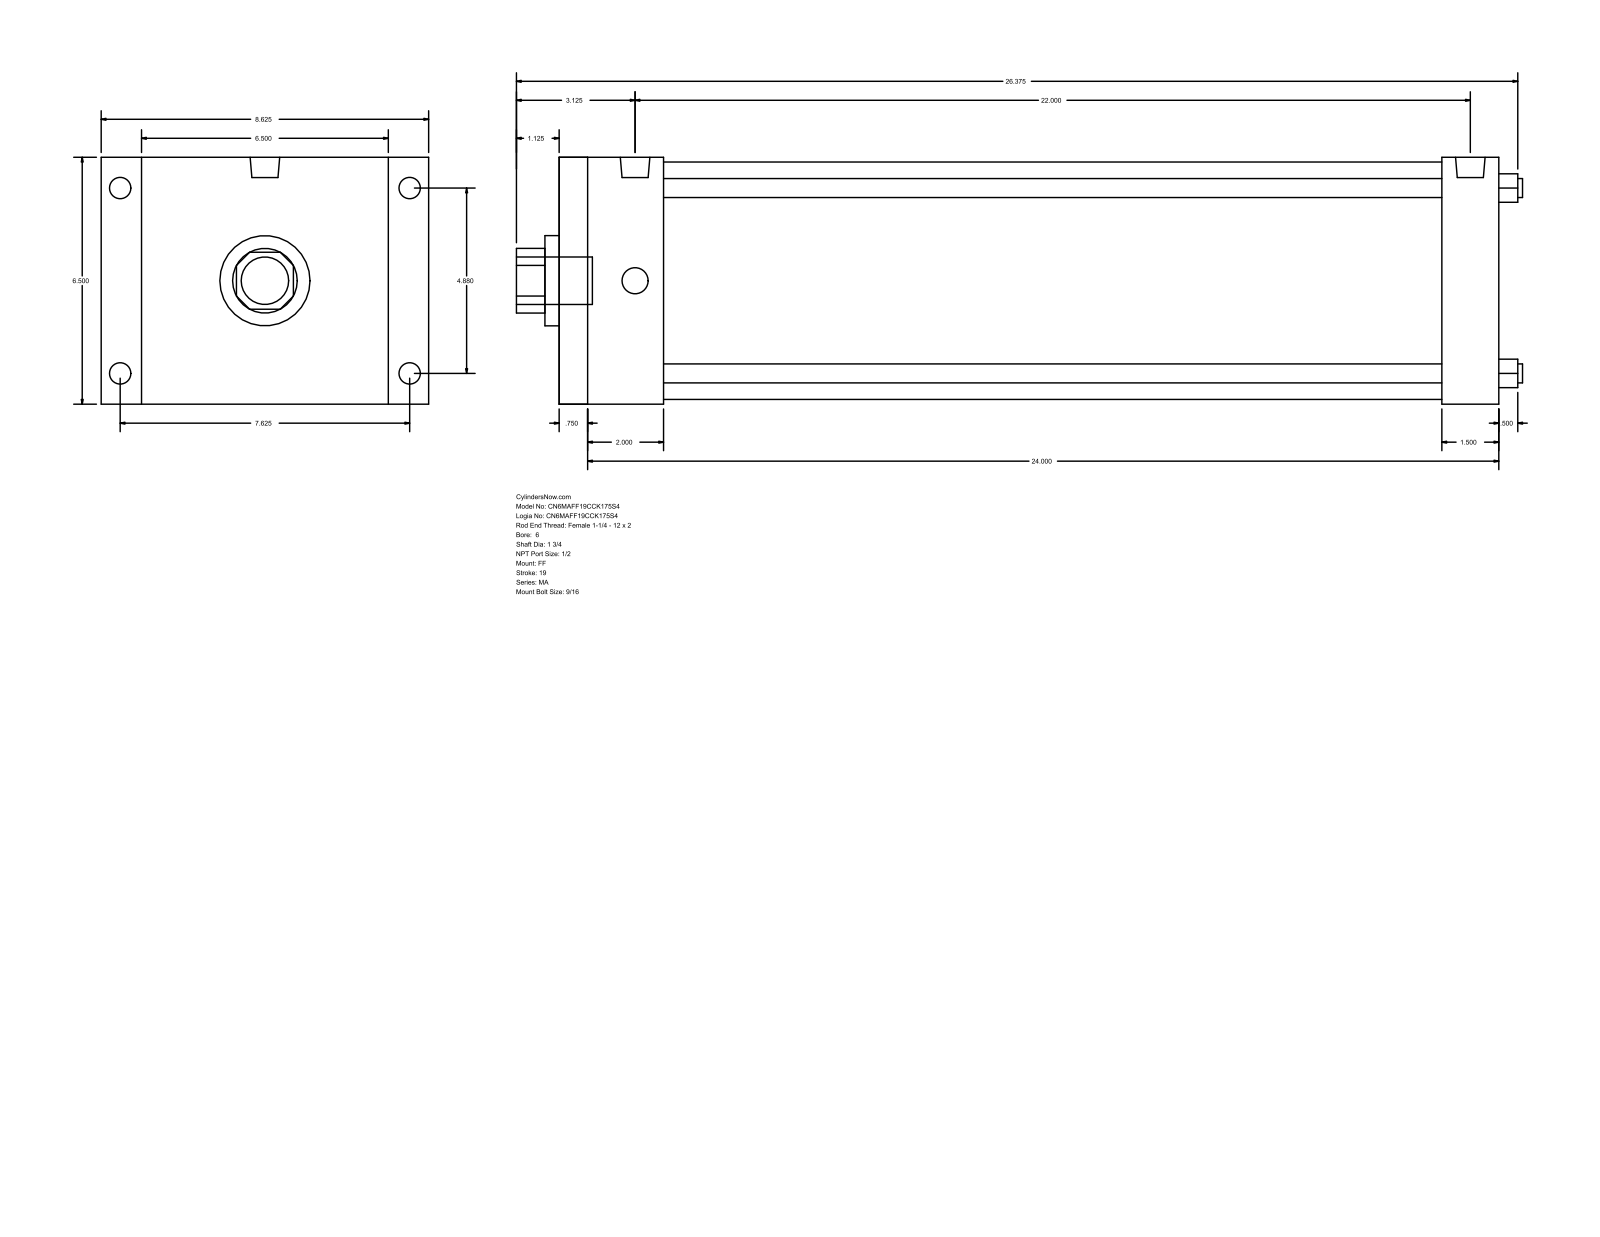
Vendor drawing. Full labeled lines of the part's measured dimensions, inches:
Part name (STEP PRODUCT): MA_FF__0600_1.75
STEP written by: GSSL Pune (CONFIG_CONTROL_DESIGN)
Units: inches
Bodies: 0 solids, 92 faces (64 planar, 28 cylindrical, 0 other)
Overall size (bounding box): 26.5 × 8.625 × 6.5
Round holes (diameter × count): ⌀0.5 ×4, ⌀1.75 ×1, ⌀2.375 ×1, ⌀6.25 ×1
Round bosses / shafts (diameter × count): ⌀0.687 ×4, ⌀0.563 ×4, ⌀0.778 ×2, ⌀1.25 ×1
Partial cylindrical surfaces — rounded edges, fillets, slot ends (radius × count): R0.852 ×1
Main face-to-face distances: 6.5, 24.75, 0.75, 24, 2, 22.5, 2.75, 22, 23.25, 20.5
Hole centre spacings: 3.451, 4.88, 6.902
